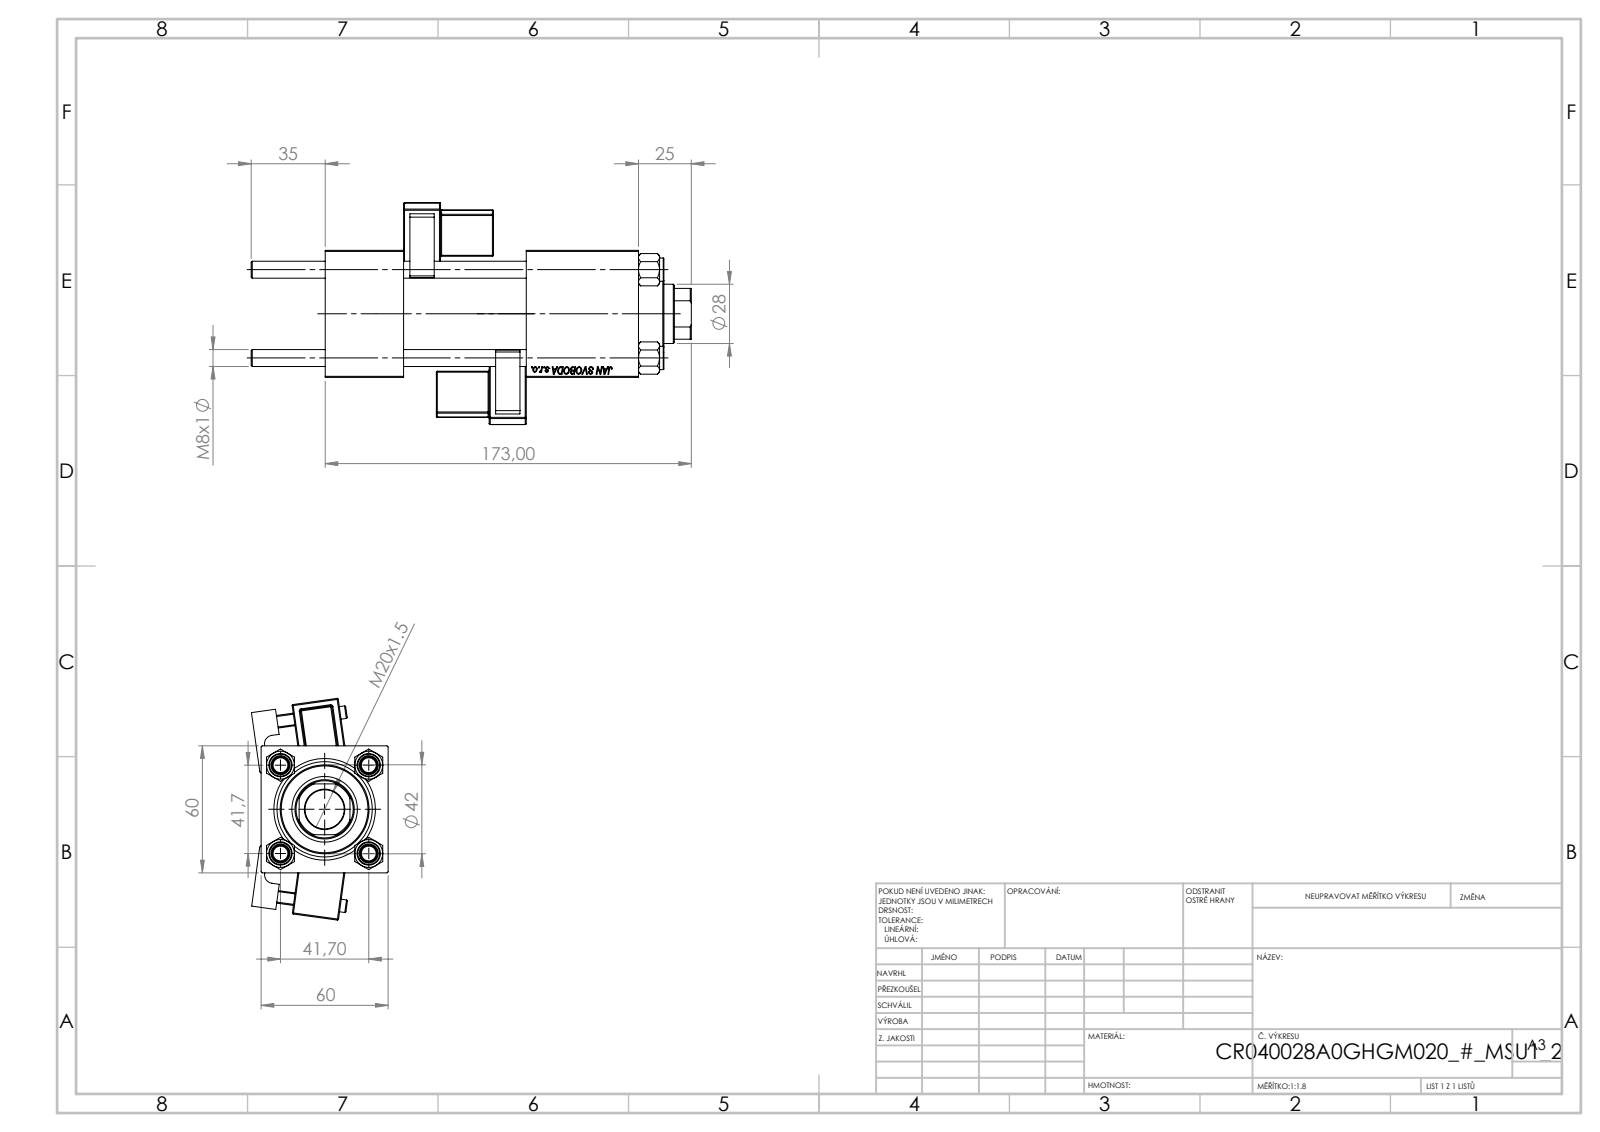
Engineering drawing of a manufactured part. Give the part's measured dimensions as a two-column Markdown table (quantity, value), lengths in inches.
| quantity | value |
| --- | --- |
| part name | NUT_M5; V215CR_MSU; V215CR_VCP; V215_VC_A (+2 more) |
| STEP written by | SolidWorks 2019 (CONFIG_CONTROL_DESIGN) |
| units | inches |
| bodies | 13 solids, 1289 faces (579 planar, 138 cylindrical, 572 other) |
| overall size | 8.189 × 4.122 × 2.543 |
| volume | 29.07 in³ |
| surface area | 204.9 in² |
| round holes (diameter × count) | 0.315 × 4, 0.276 × 2, 0.656 × 2, 0.945 × 2, 0.728 × 1, 1.102 × 1, 1.22 × 1, 1.575 × 1, 1.772 × 1 |
| round bosses / shafts (diameter × count) | 0.433 × 4, 0.236 × 2, 1.811 × 1, 1.654 × 1 |
| partial cylindrical surfaces (radius × count) | 0.02 × 48, 0.039 × 2, 0.098 × 2, 0.157 × 2, 0.531 × 1 |
| main face-to-face distances | 2.362, 1.457, 2.283, 3.74, 2.087, 5.827, 4.37, 4.697, 3.24, 0.957 |
| hole center spacings | 1.161, 1.642, 2.322, 3.642 |
